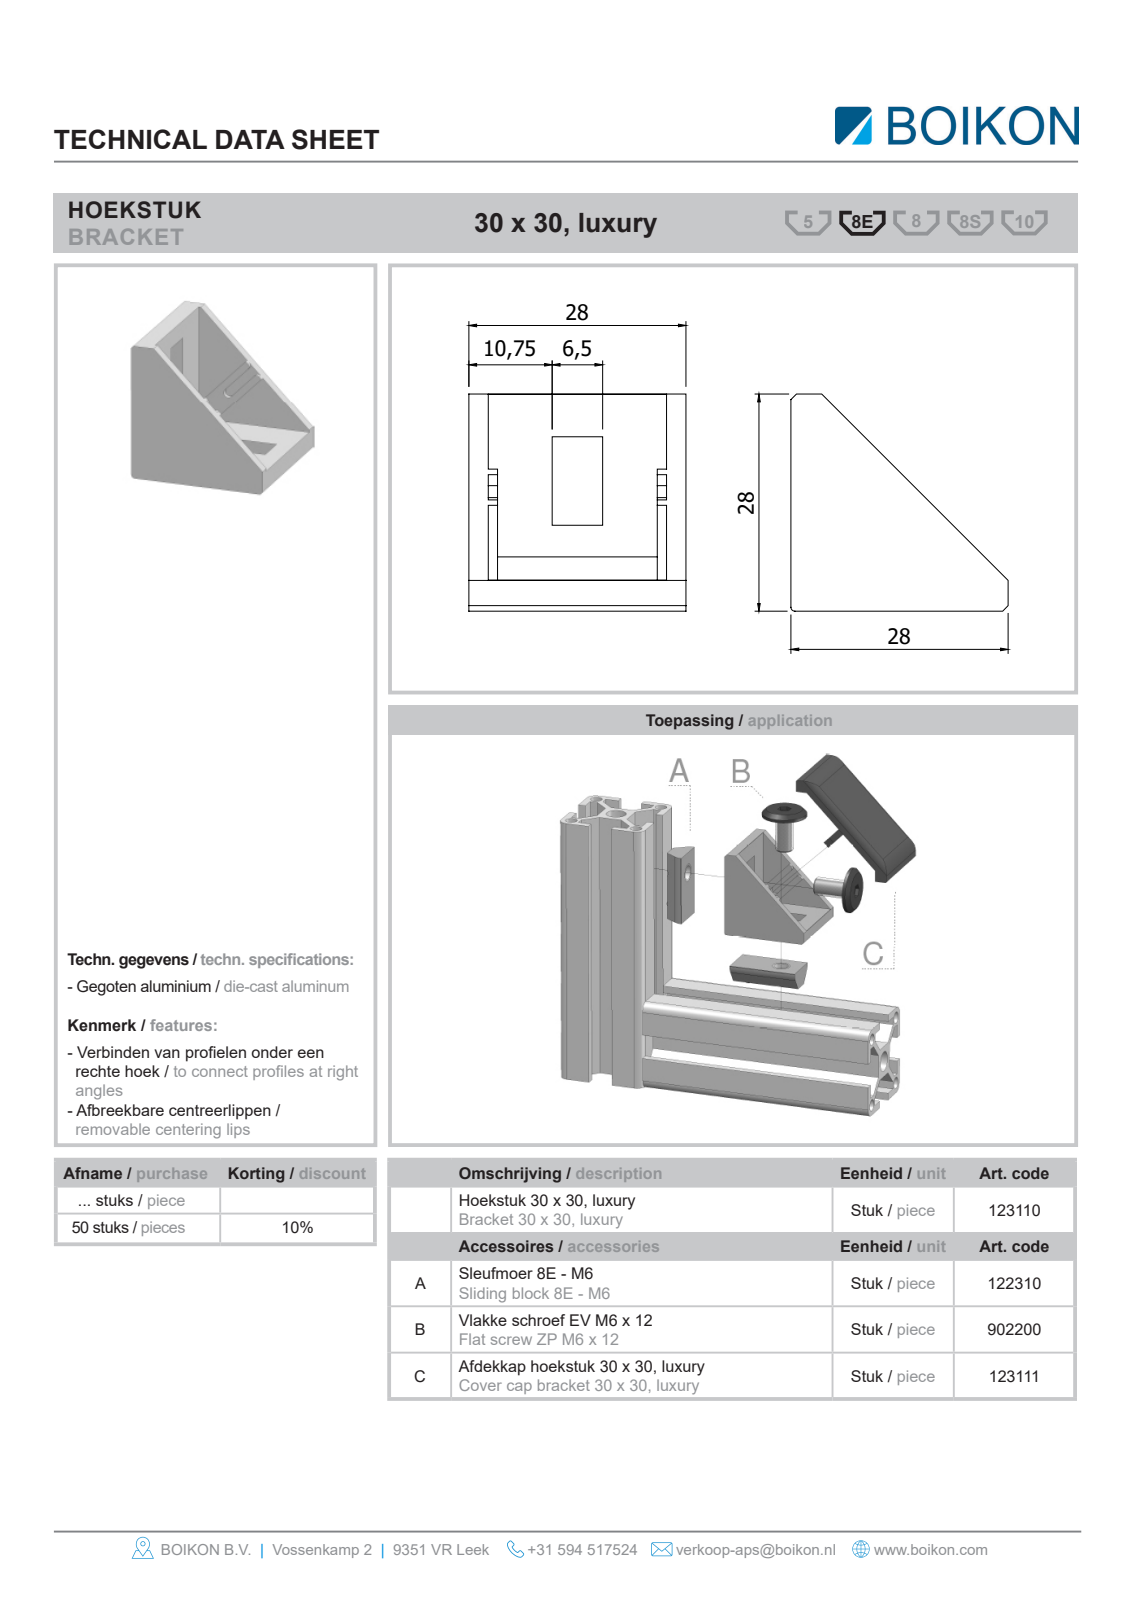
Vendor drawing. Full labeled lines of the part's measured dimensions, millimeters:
Part name (STEP PRODUCT): Root; 123110HOEKSTUK 30X30 LUXURYBOIKON; 902200Vlakke schroef M6x12BOIKON; 122310Sleufmoer 8E - M6 met kogelBOIKON (+1 more)
STEP written by: HiCAD 2013 1802.4 Build 509 (AUTOMOTIVE_DESIGN)
Units: millimetres
Bodies: 6 solids, 183 faces (156 planar, 23 cylindrical, 4 other)
Overall size (bounding box): 41.73 × 41.73 × 28
Volume: 13 461 mm³ · Surface area: 11 473 mm²
Round holes (diameter × count): ⌀6 ×2
Round bosses / shafts (diameter × count): ⌀15 ×2, ⌀4.77 ×2
Partial cylindrical surfaces — rounded edges, fillets, slot ends (radius × count): R4 ×4, R1 ×2, R2 ×2, R7 ×2, R0.5 ×1, R1.3 ×1, R3 ×1
Main face-to-face distances: 4, 3, 2.4, 28, 6.4, 1, 2.5, 25.5, 23, 24
